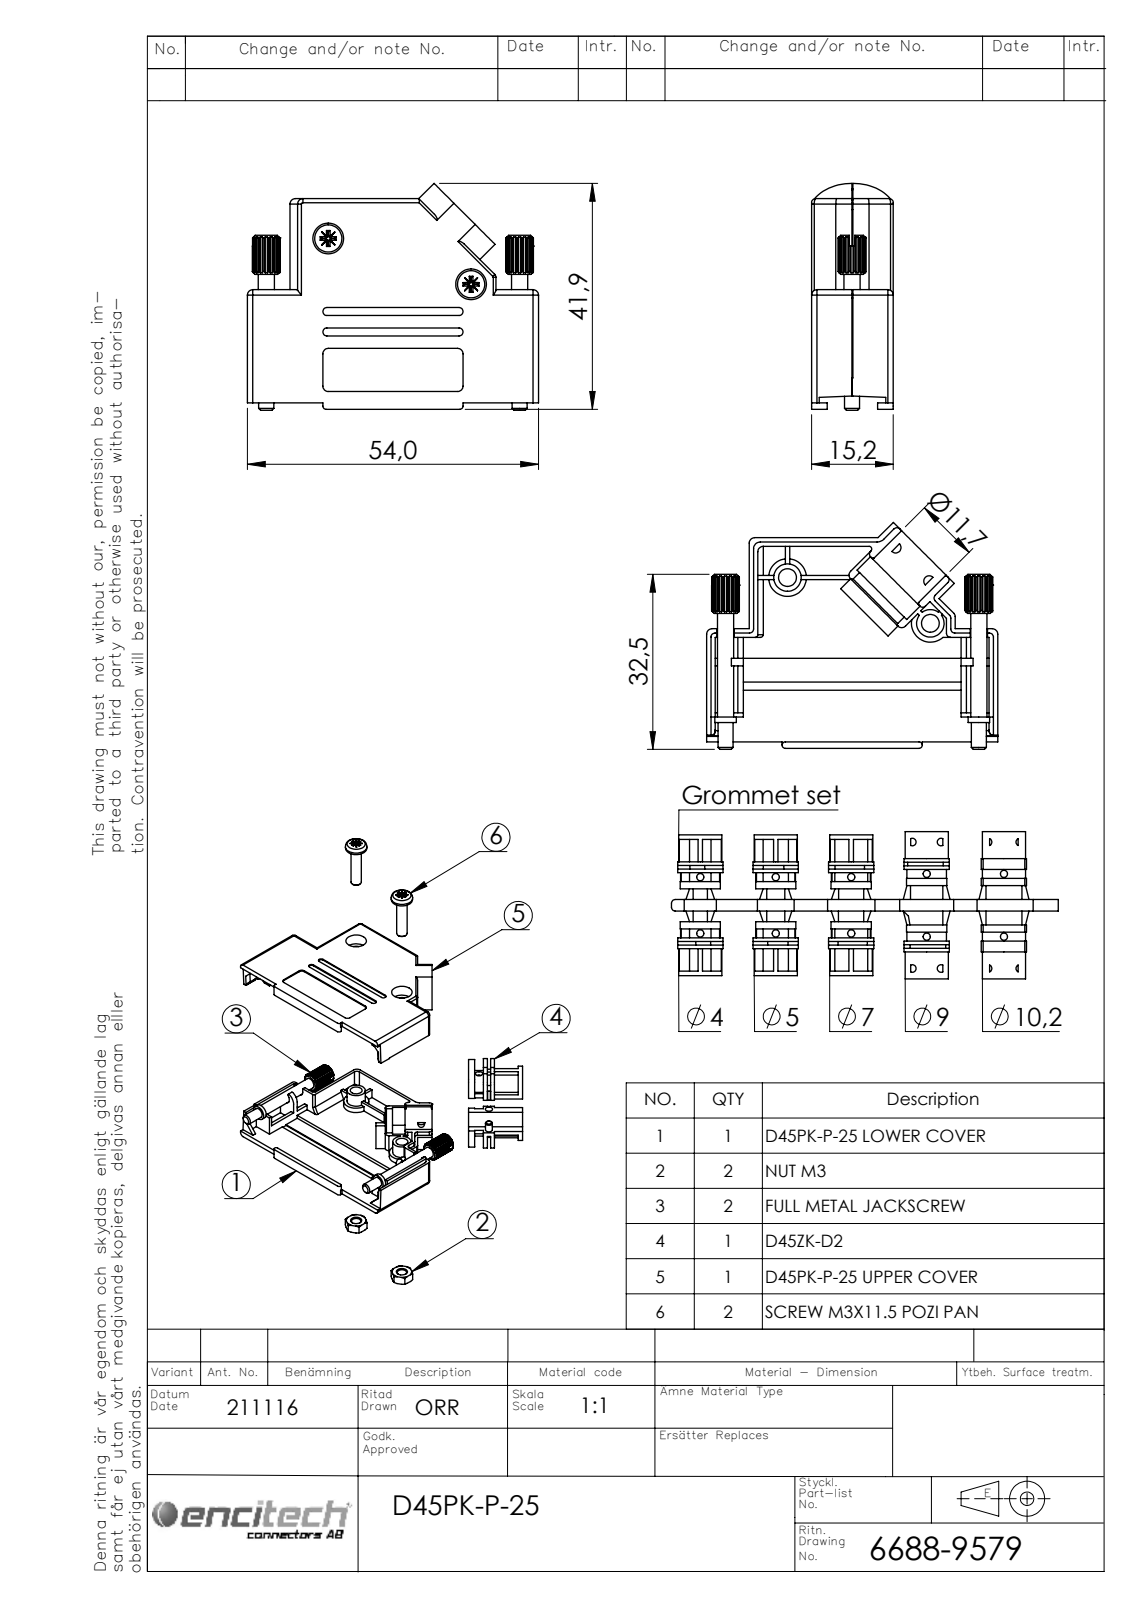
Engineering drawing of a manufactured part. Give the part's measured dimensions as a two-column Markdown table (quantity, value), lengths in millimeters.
| quantity | value |
| --- | --- |
| part name | 6855-0304-11; 6688-9579; 6855-0303-11; 6826-0142-03 (+3 more) |
| STEP written by | SolidWorks 2021 (AUTOMOTIVE_DESIGN) |
| units | millimeters |
| bodies | 10 solids, 965 faces (587 planar, 268 cylindrical, 110 other) |
| overall size | 54 × 42.13 × 15.15 |
| volume | 10 515 mm³ |
| surface area | 15 432 mm² |
| round holes (diameter × count) | 2 × 3, 2.6 × 2, 3.3 × 2, 5.7 × 2, 7 × 1 |
| round bosses / shafts (diameter × count) | 5.1 × 2, 4 × 2, 3 × 2, 2.9 × 2, 2.8 × 2, 1.9 × 2, 11.6 × 1, 9.2 × 1 |
| partial cylindrical surfaces (radius × count) | 1 × 25, 0.75 × 21, 0.5 × 16, 0.1 × 8, 1.6 × 4, 5.91 × 4, 0.33 × 2, 0.6 × 2 |
| main face-to-face distances | 1.4, 13.75, 15.15, 1, 1.6, 2.4, 12.75, 11.35, 12.35, 1.1 |
| hole center spacings | 5.71, 5.19, 10.01, 10.76, 15.13, 15.21, 17.2, 22.9 |
